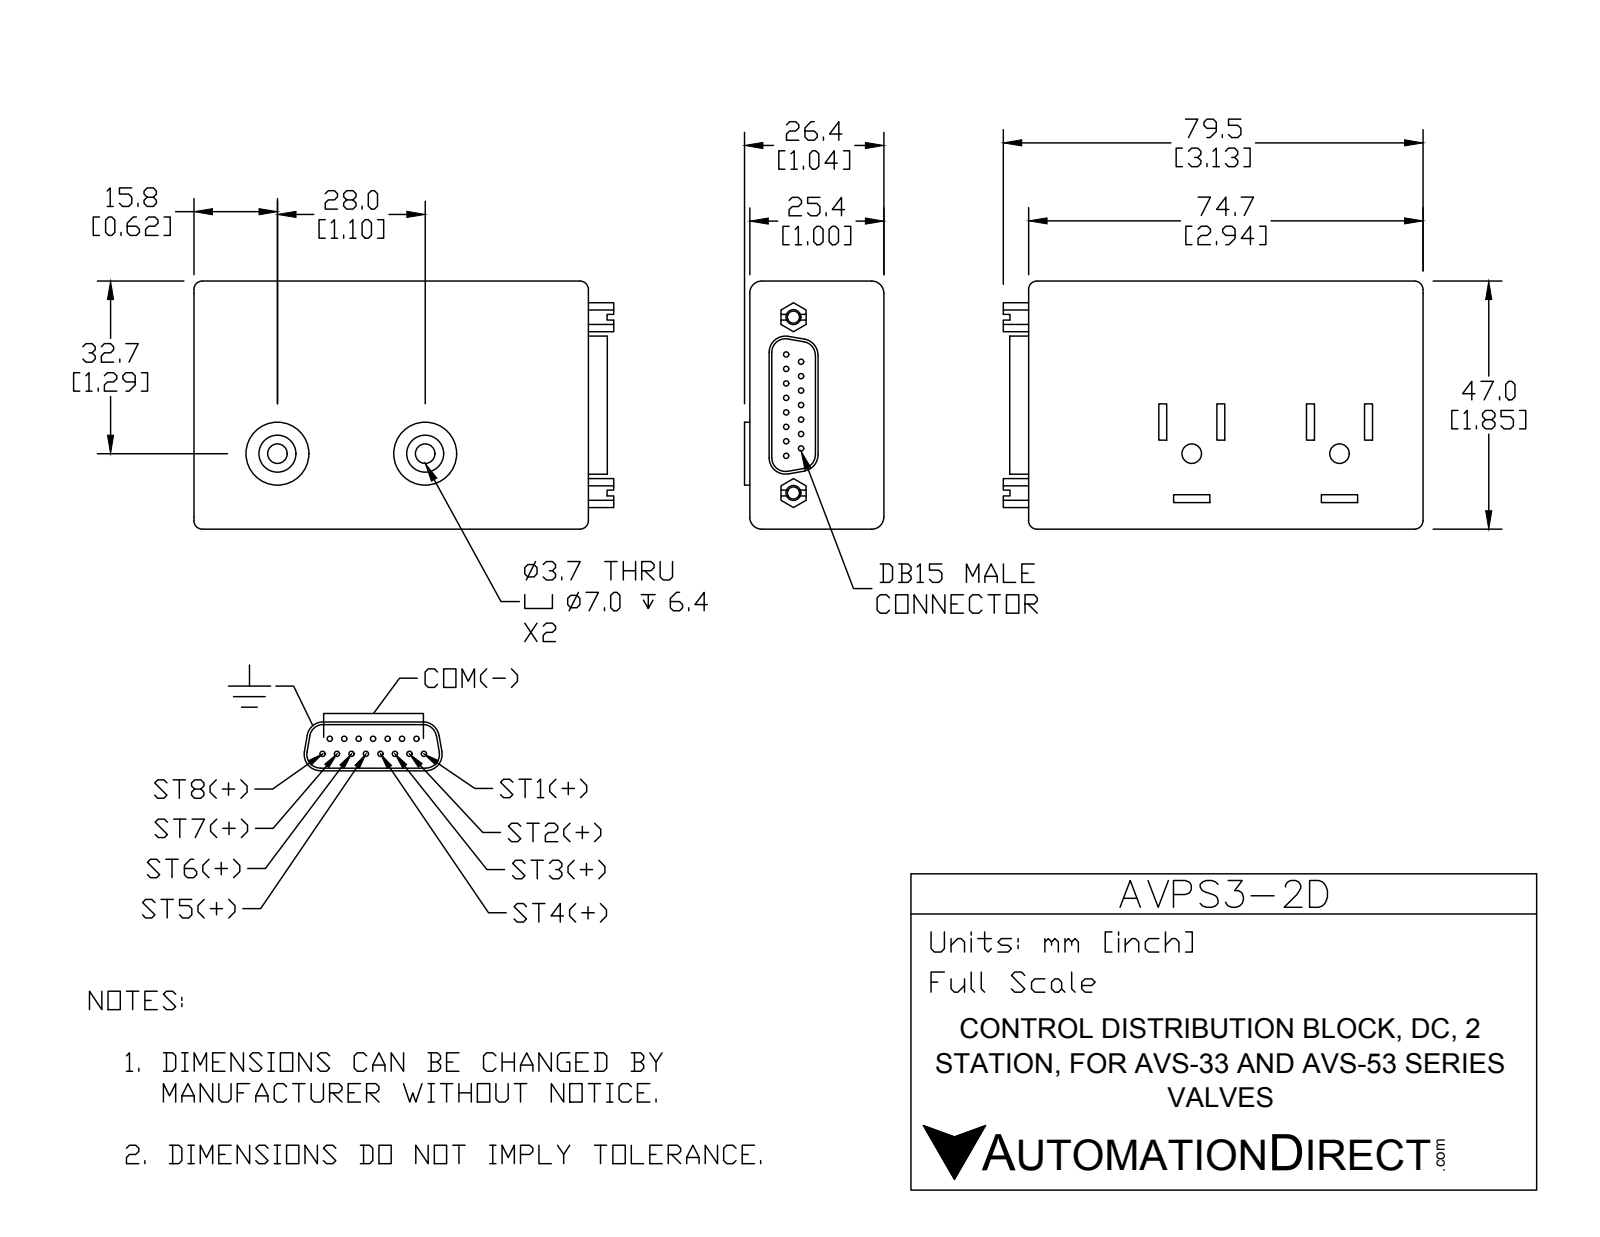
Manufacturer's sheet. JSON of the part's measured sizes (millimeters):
{"part_name": "AVPS3-2D", "step_written_by": "SolidWorks 2016 (AUTOMOTIVE_DESIGN)", "units": "millimeters", "bodies": {"solids": 1, "faces": 173, "planar": 93, "cylindrical": 68, "other": 12}, "overall_size": [79.5, 47, 26.4], "volume_mm3": 87340, "surface_area_mm2": 15250, "round_holes": [[2.3, 2], [3.7, 2], [7, 2]], "round_bosses_or_shafts": [[1, 15], [11.9, 2]], "partial_cylinders_radius": [[1.6, 6], [2.3, 4], [2.6, 4], [3.1, 4], [1.6, 2]], "face_to_face_distances": [25.4, 47, 74.7, 1.5, 28, 3.1, 71.6, 11, 0.5, 1], "hole_center_spacings": [28, 33.3]}
